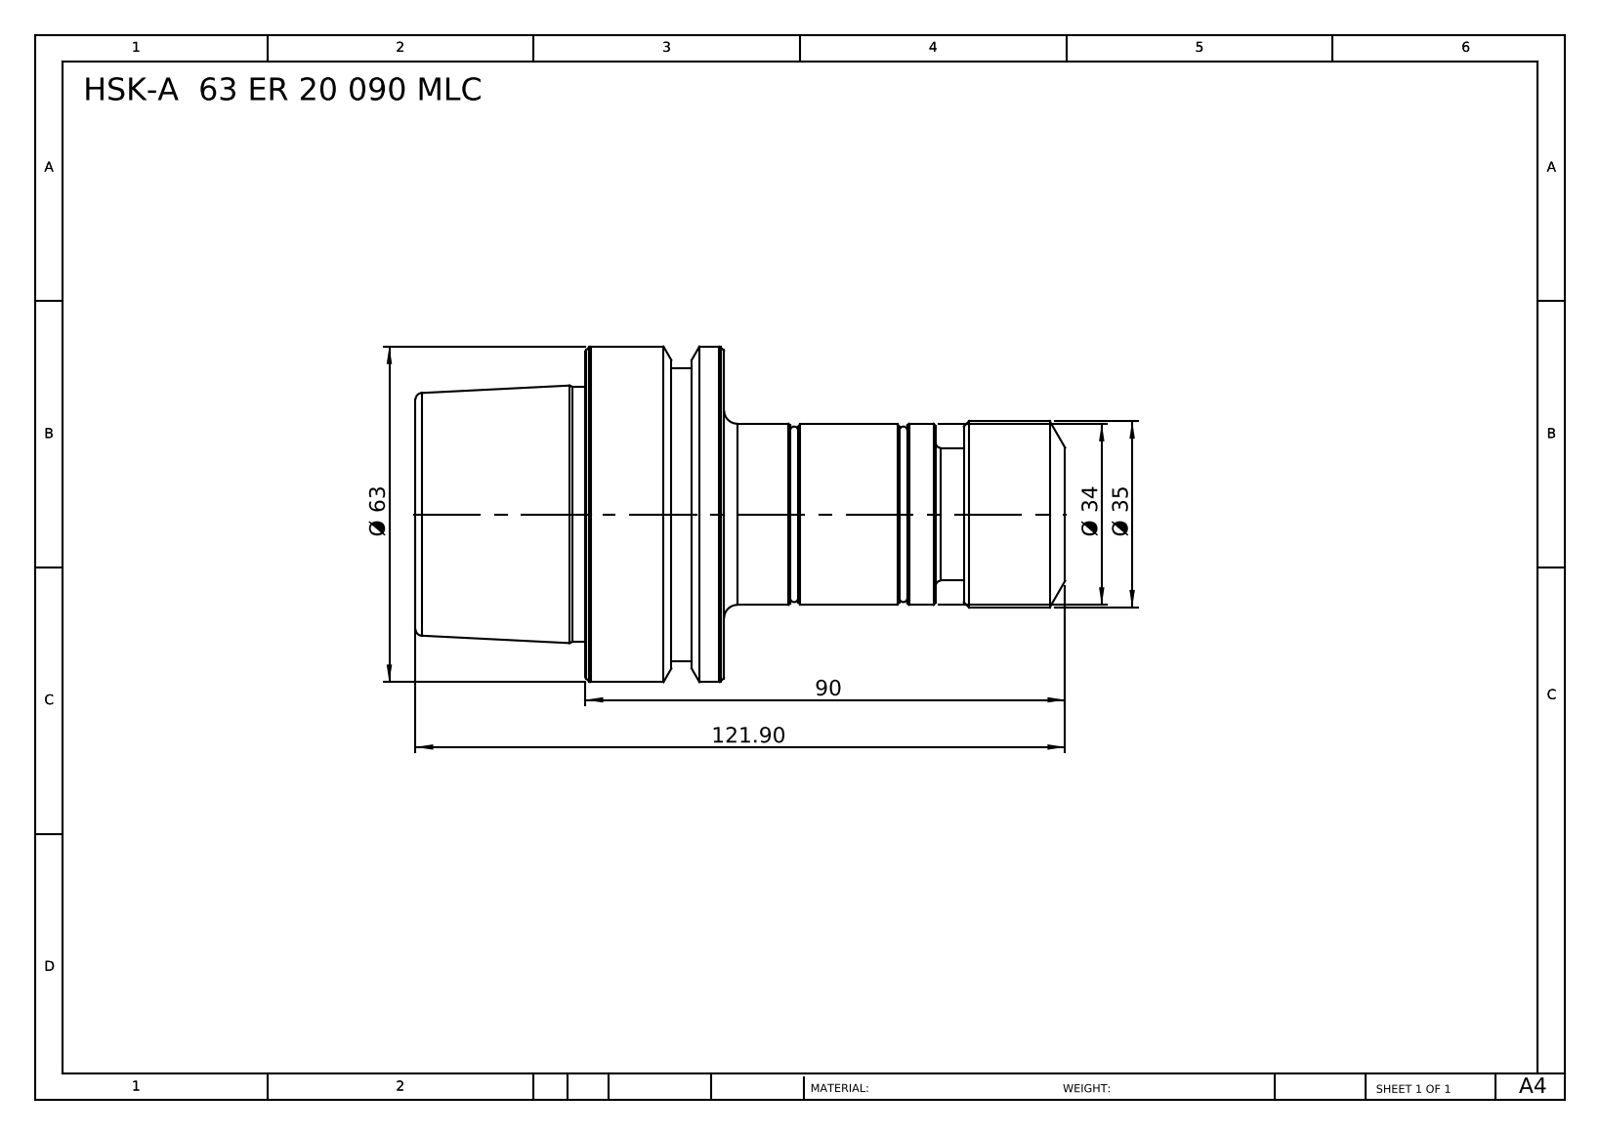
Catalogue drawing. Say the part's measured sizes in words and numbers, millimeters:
The part is named "HSK-A 63 ER 20 090 MLC". Its 3-D file was written by "SolidWorks 2014 (CONFIG_CONTROL_DESIGN)". It is 1 solid with 78 faces: 12 planar, 18 cylindrical and 48 other. Overall it measures 121.9 by 63 by 63 millimeters. Its volume is 188 417 cubic millimeters and its surface area 24 418 square millimeters. Round bosses or shafts: 1 of diameter 63, 1 of diameter 55, 1 of diameter 47.78, 1 of diameter 35, 1 of diameter 34, 1 of diameter 33.8, 1 of diameter 24.9. The main face-to-face distances are 57.9, 26, 31.9, 64, 90, 121.9, 19, 5.3, 45, 71.
